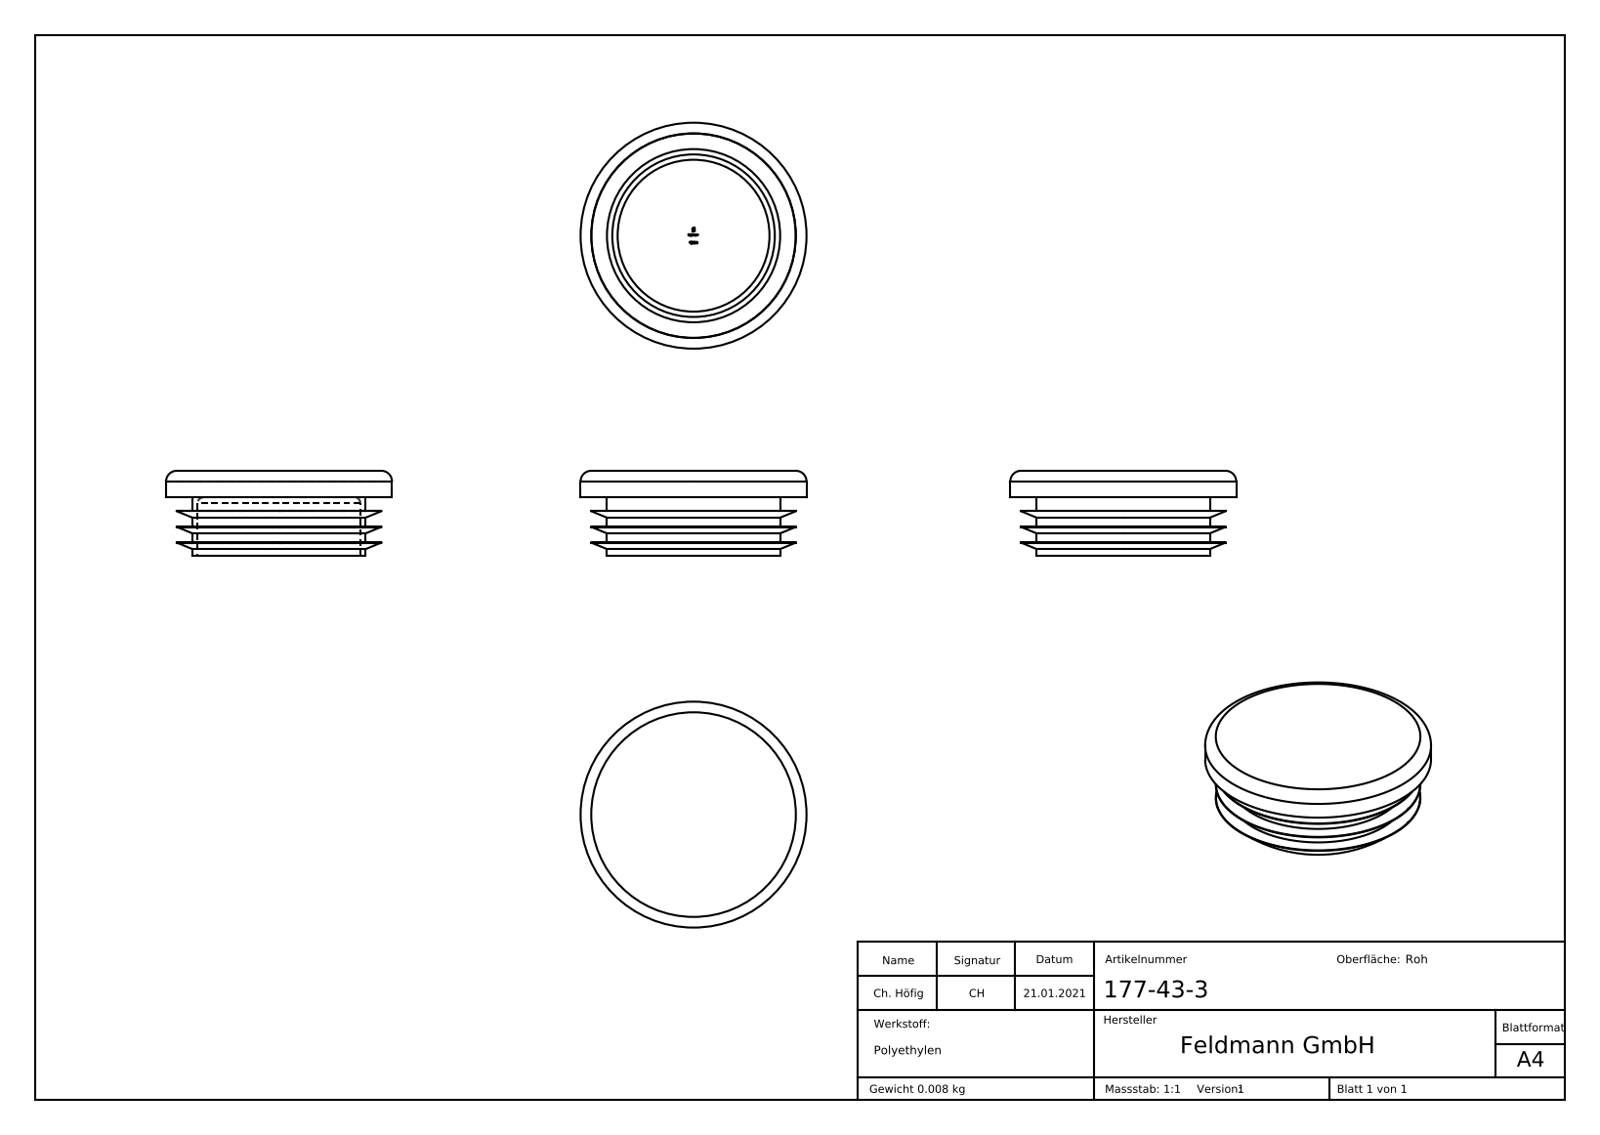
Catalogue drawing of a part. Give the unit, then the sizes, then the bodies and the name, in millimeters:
Units: millimetres
Overall size (bounding box): 42.4 × 42.4 × 16.5
Round holes (diameter × count): ⌀31.4 ×1
Round bosses / shafts (diameter × count): ⌀42.4 ×1, ⌀33.4 ×1
Main face-to-face distances: 5, 3, 6, 9, 14, 11, 8, 2.5, 5.5, 8.5
Volume: 8 271 mm³ · Surface area: 6 883 mm²
Bodies: 1 solid, 222 faces (126 planar, 12 cylindrical, 84 other)
Part name (STEP PRODUCT): 177-43-3
STEP written by: SolidWorks 2015 (CONFIG_CONTROL_DESIGN)
